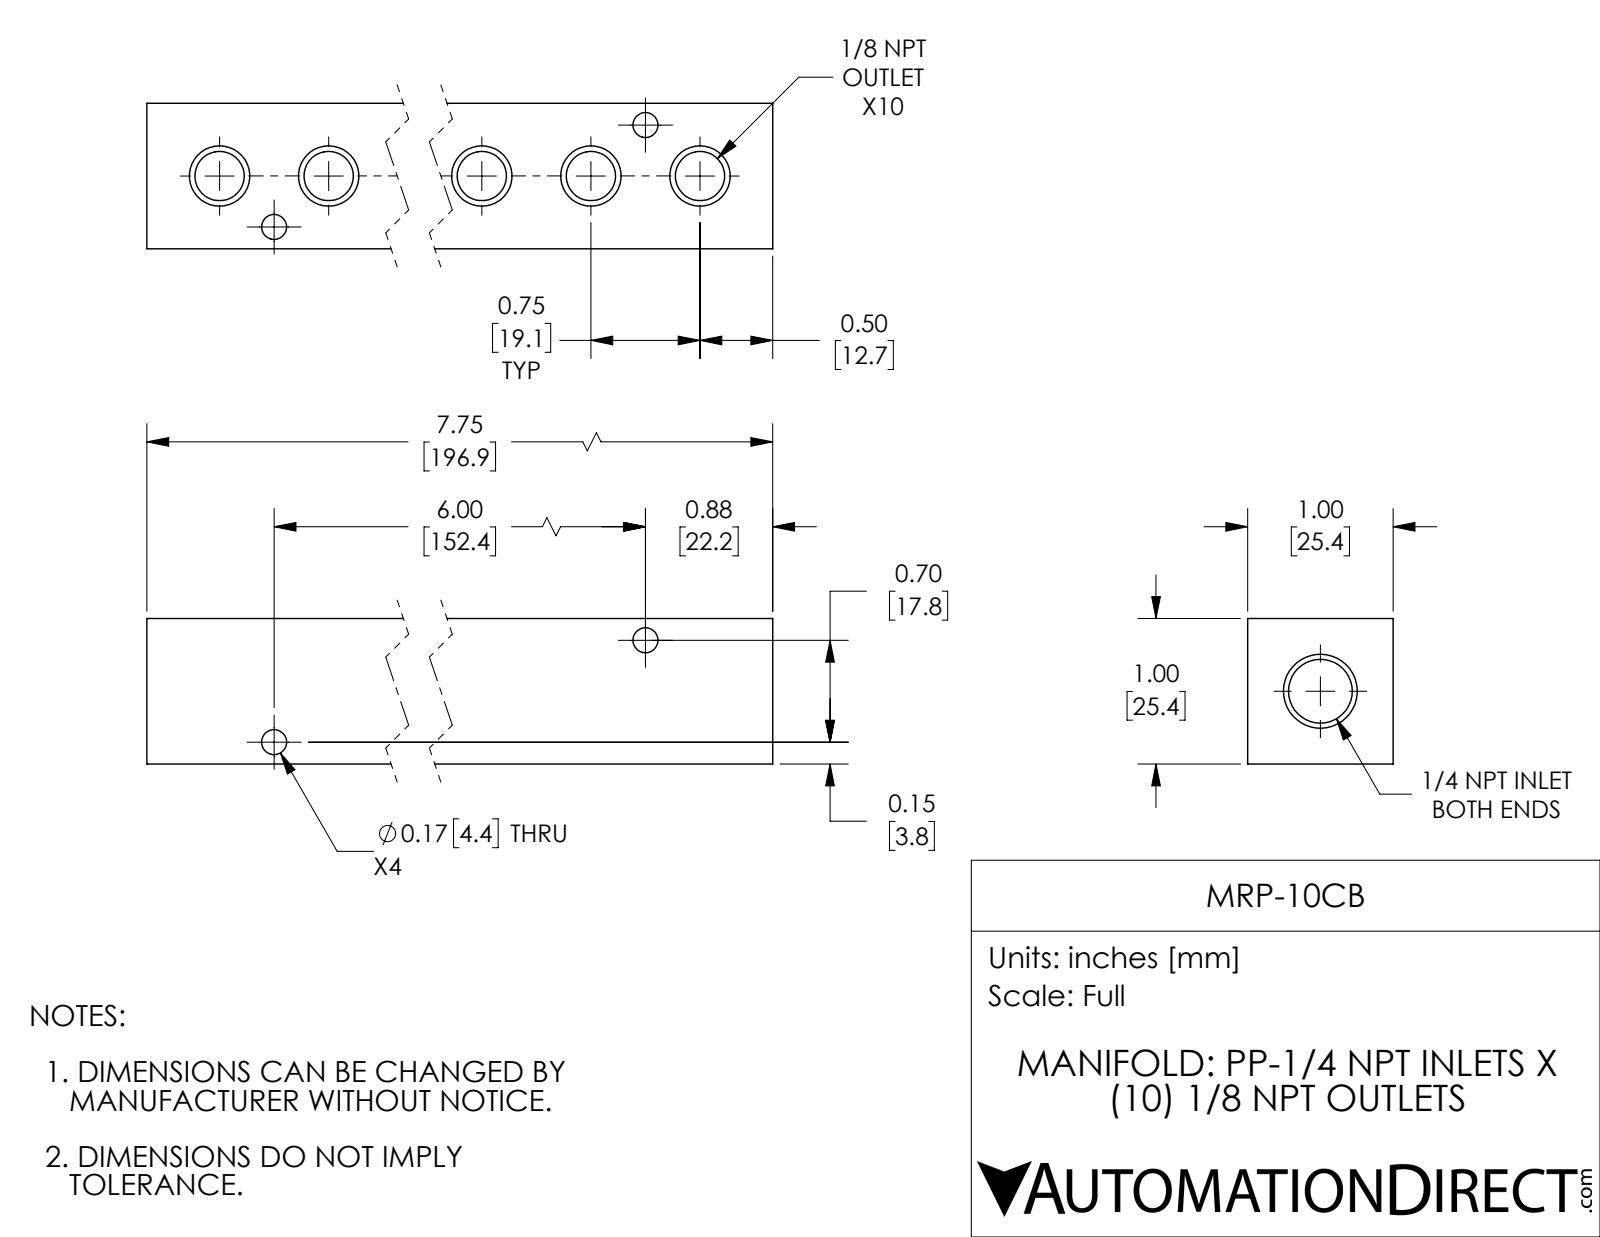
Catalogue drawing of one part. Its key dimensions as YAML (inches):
part_name: "MRP-10CB"
step_written_by: "SolidWorks 2018 (AUTOMOTIVE_DESIGN)"
units: inches
bodies: {solids: 1, faces: 68, planar: 6, cylindrical: 38, other: 24}
overall_size: [7.75, 1, 1]
volume: 6.216
surface_area: 46.33
round_holes:
  - {diameter: 0.339, count: 10}
  - {diameter: 0.172, count: 4}
  - {diameter: 0.438, count: 1}
face_to_face_distances: [1, 7.75]
hole_center_spacings: [0.75, 1.5, 2.25, 3, 3.75, 0.513, 4.5, 5.25]
